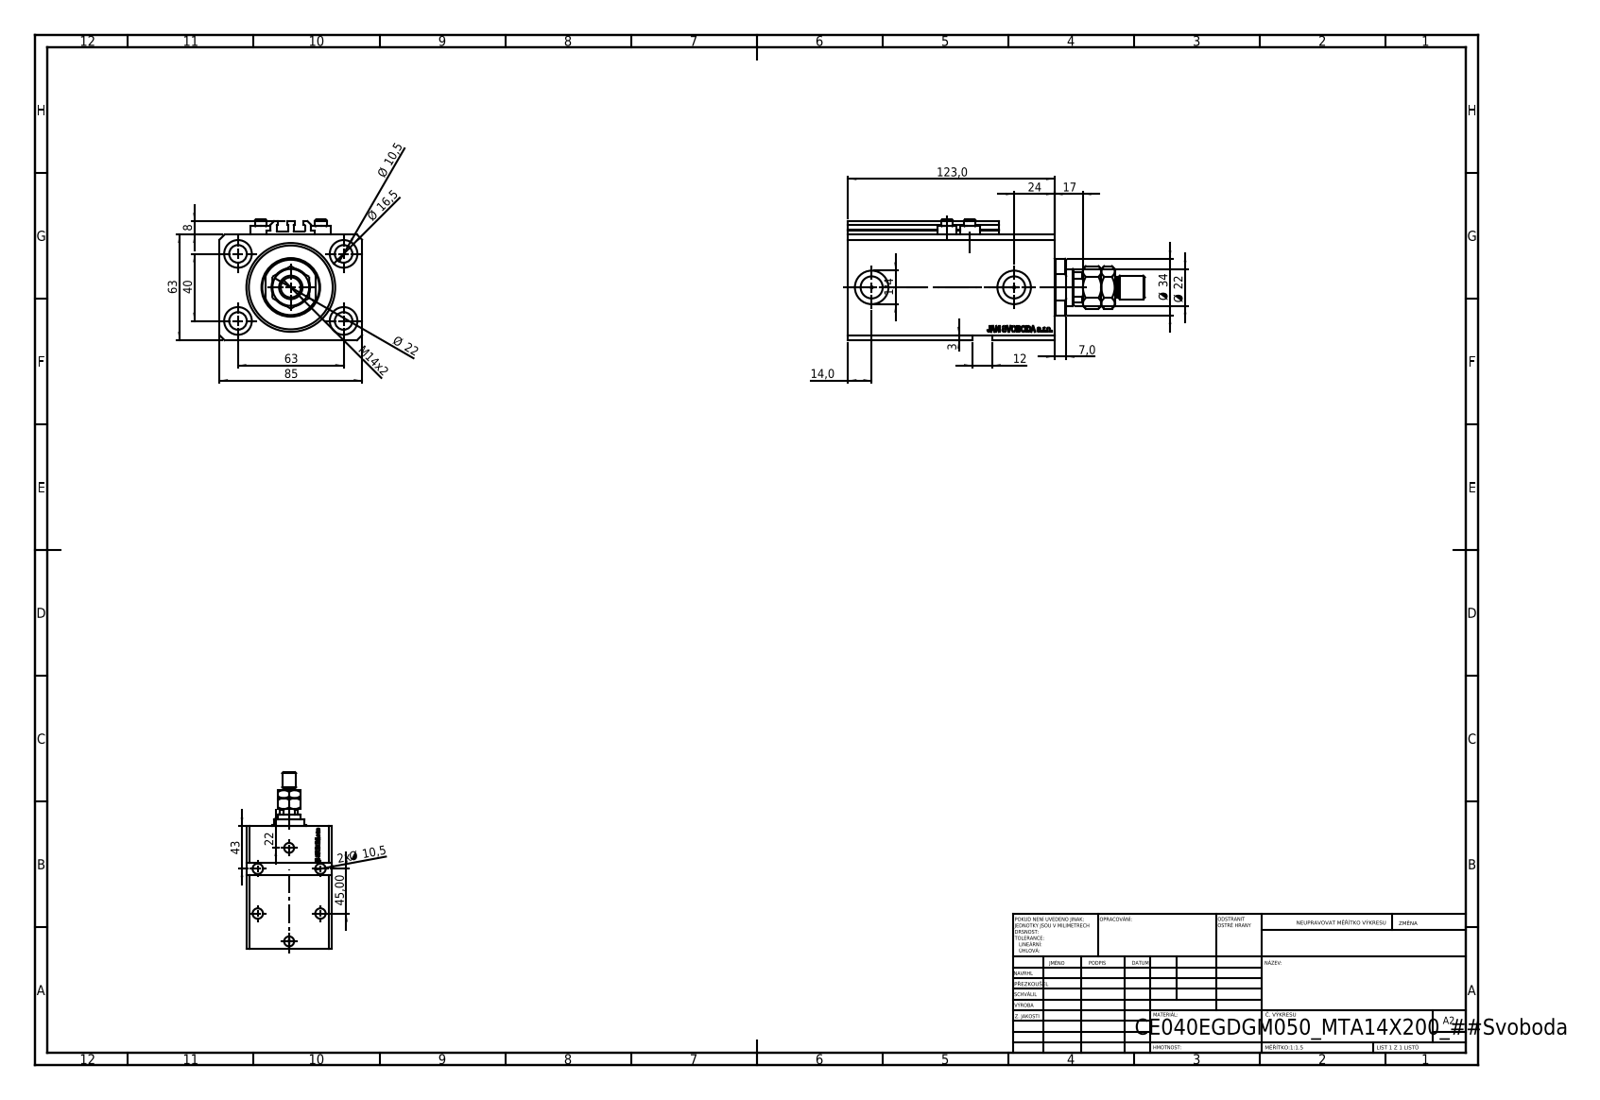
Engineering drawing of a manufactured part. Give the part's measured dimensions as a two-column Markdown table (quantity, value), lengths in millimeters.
| quantity | value |
| --- | --- |
| part name | ALLEN BOLT V250CE; V250CE_VC_E; MTA; V250CE_C_VCP (+1 more) |
| STEP written by | SolidWorks 2019 (CONFIG_CONTROL_DESIGN) |
| units | millimeters |
| bodies | 9 solids, 1172 faces (554 planar, 162 cylindrical, 456 other) |
| overall size | 177 × 85 × 72 |
| volume | 563 556 mm³ |
| surface area | 123 526 mm² |
| round holes (diameter × count) | 10.5 × 8, 1.25 × 4, 4 × 4, 16.5 × 4, 10 × 2, 13.16 × 2, 20 × 2, 12.5 × 1, 22 × 1, 40 × 1, 53 × 1 |
| round bosses / shafts (diameter × count) | 11.6 × 4, 7 × 4, 34 × 1, 14 × 1, 12 × 1 |
| partial cylindrical surfaces (radius × count) | 0.2 × 10, 10.5 × 1 |
| main face-to-face distances | 63, 85, 17, 123, 106, 11.4, 94.6, 111.6, 3, 65 |
| hole center spacings | 37.31, 63, 13.6, 15.4, 24.96, 27.54, 33.62, 36 |
